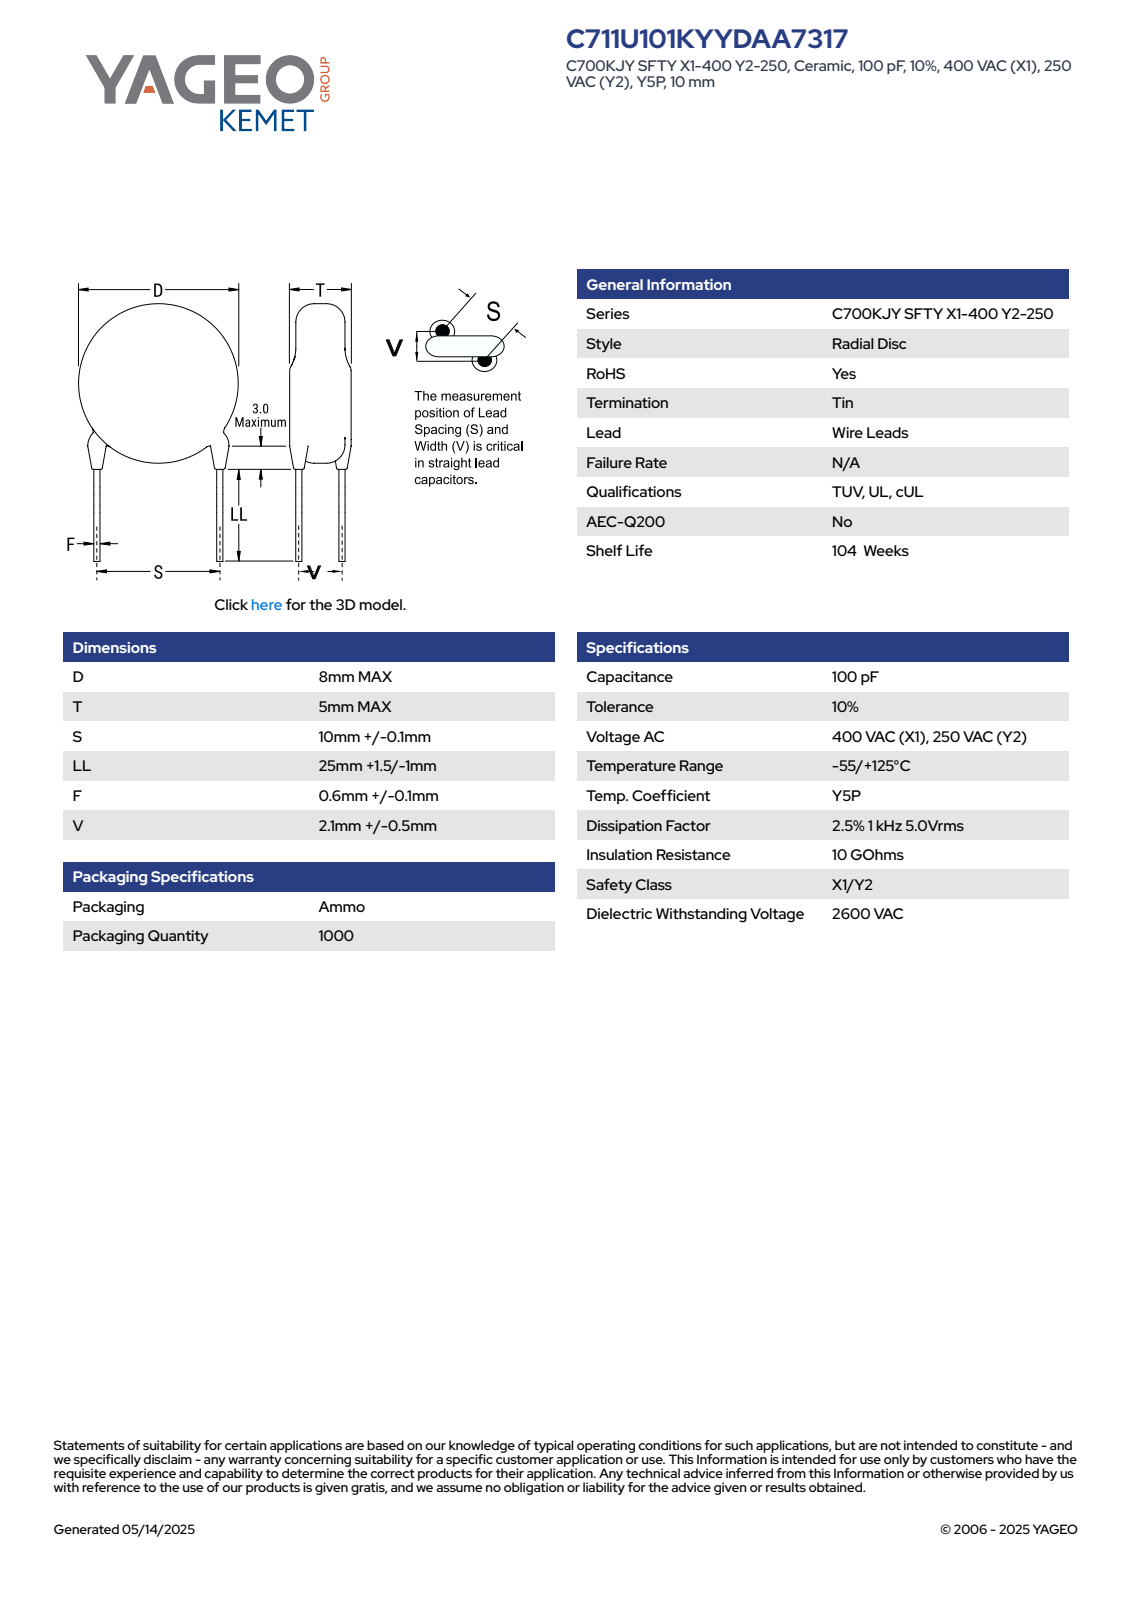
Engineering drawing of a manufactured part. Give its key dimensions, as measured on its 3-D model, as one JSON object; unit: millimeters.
{"part_name": "CCD_KST_8X5_D8T5S10.1LL26.5F0.7V2.1", "step_written_by": "SolidWorks 2021 (AUTOMOTIVE_DESIGN)", "units": "millimeters", "bodies": {"solids": 4, "faces": 81, "planar": 63, "cylindrical": 14, "other": 4}, "overall_size": [36, 11.2, 5], "volume_mm3": 272, "surface_area_mm2": 361, "round_bosses_or_shafts": [[1.2, 4], [0.7, 2], [8, 1]], "face_to_face_distances": [5, 26.5, 0.97, 32.52, 6.02, 31.55, 5.05, 0.36, 0.78, 3.96]}
